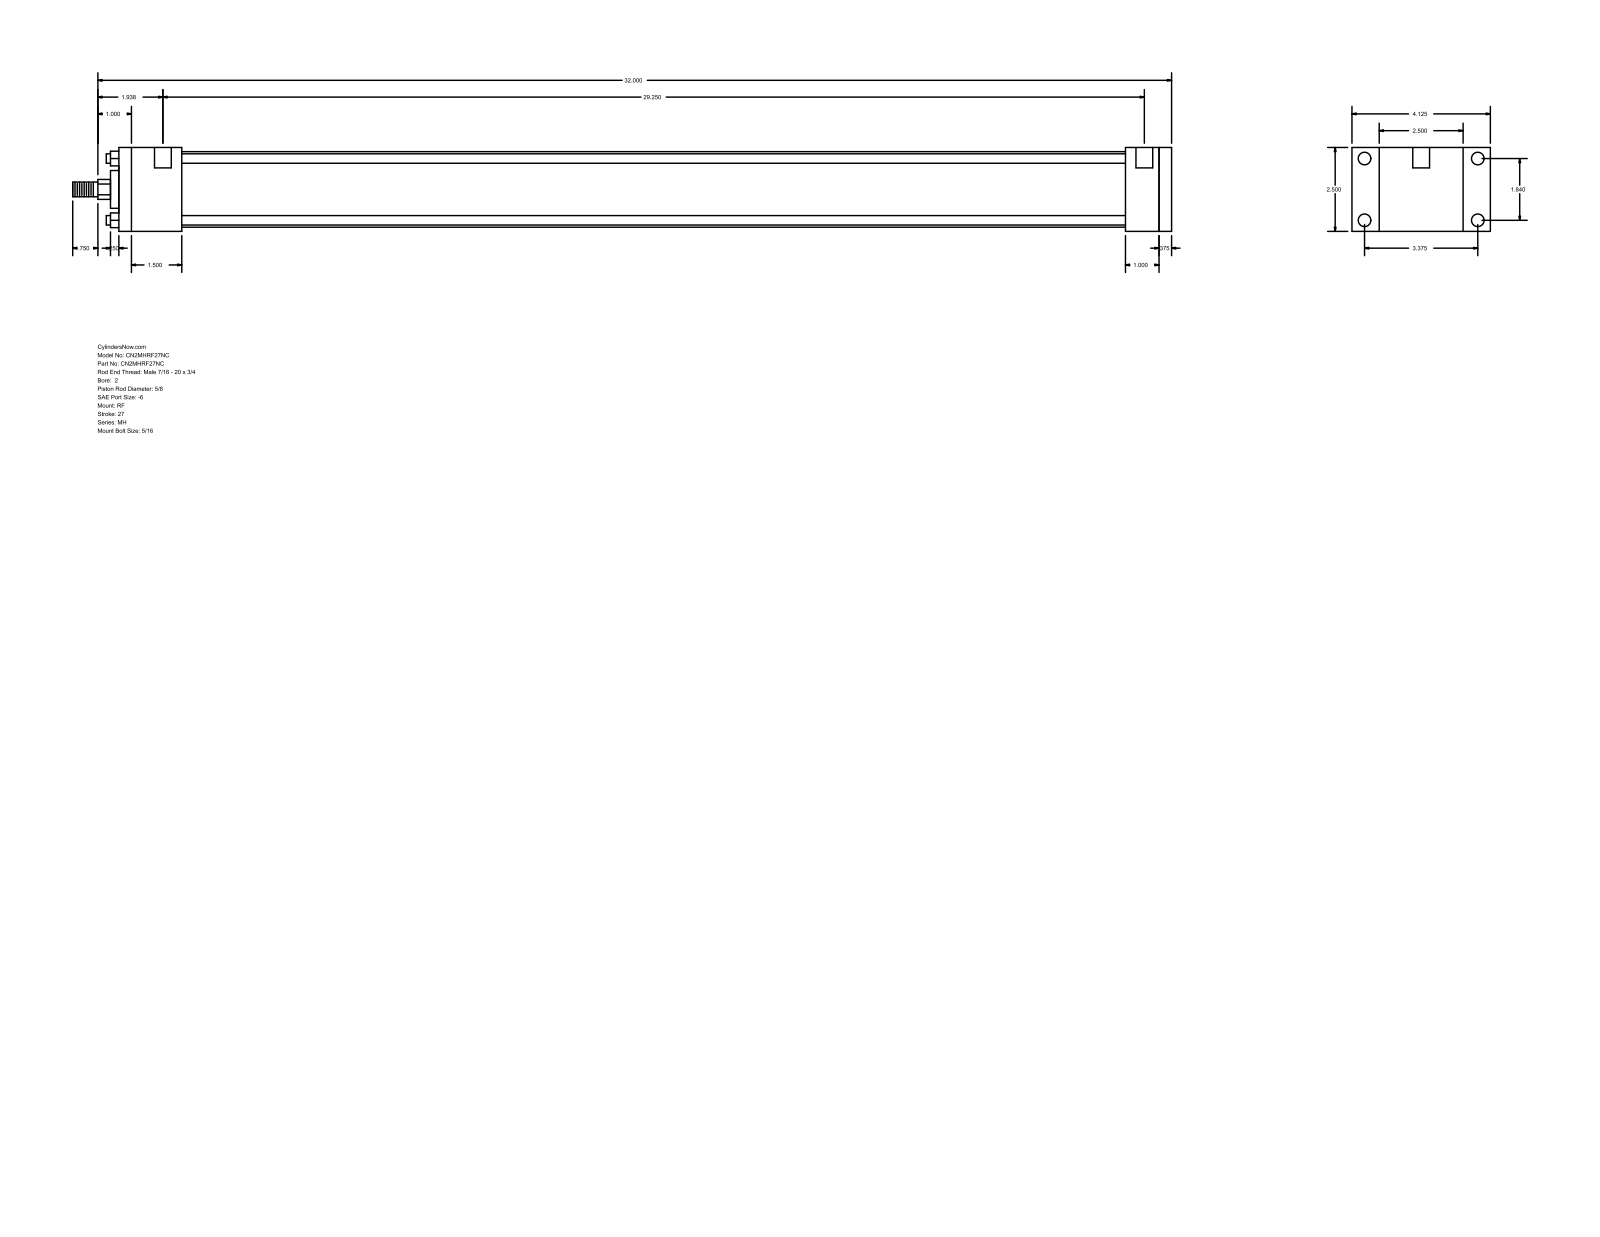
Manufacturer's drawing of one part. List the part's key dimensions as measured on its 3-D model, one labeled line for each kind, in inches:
Part name (STEP PRODUCT): MH_RF__0200_0.625
STEP written by: GSSL Pune (CONFIG_CONTROL_DESIGN)
Units: inches
Bodies: 0 solids, 92 faces (64 planar, 28 cylindrical, 0 other)
Overall size (bounding box): 32.75 × 4.125 × 2.5
Round holes (diameter × count): ⌀0.219 ×4, ⌀0.375 ×4, ⌀0.5 ×2
Round bosses / shafts (diameter × count): ⌀0.281 ×4, ⌀2.25 ×1, ⌀1.125 ×1, ⌀0.625 ×1, ⌀0.437 ×1
Partial cylindrical surfaces — rounded edges, fillets, slot ends (radius × count): R0.297 ×1
Main face-to-face distances: 2.5, 31.375, 0.375, 31, 1.875, 30, 28.125, 29.125, 29.5, 1
Hole centre spacings: 1.84, 3.375, 3.844, 29.563, 0.125, 0.187, 29.25, 29.375
